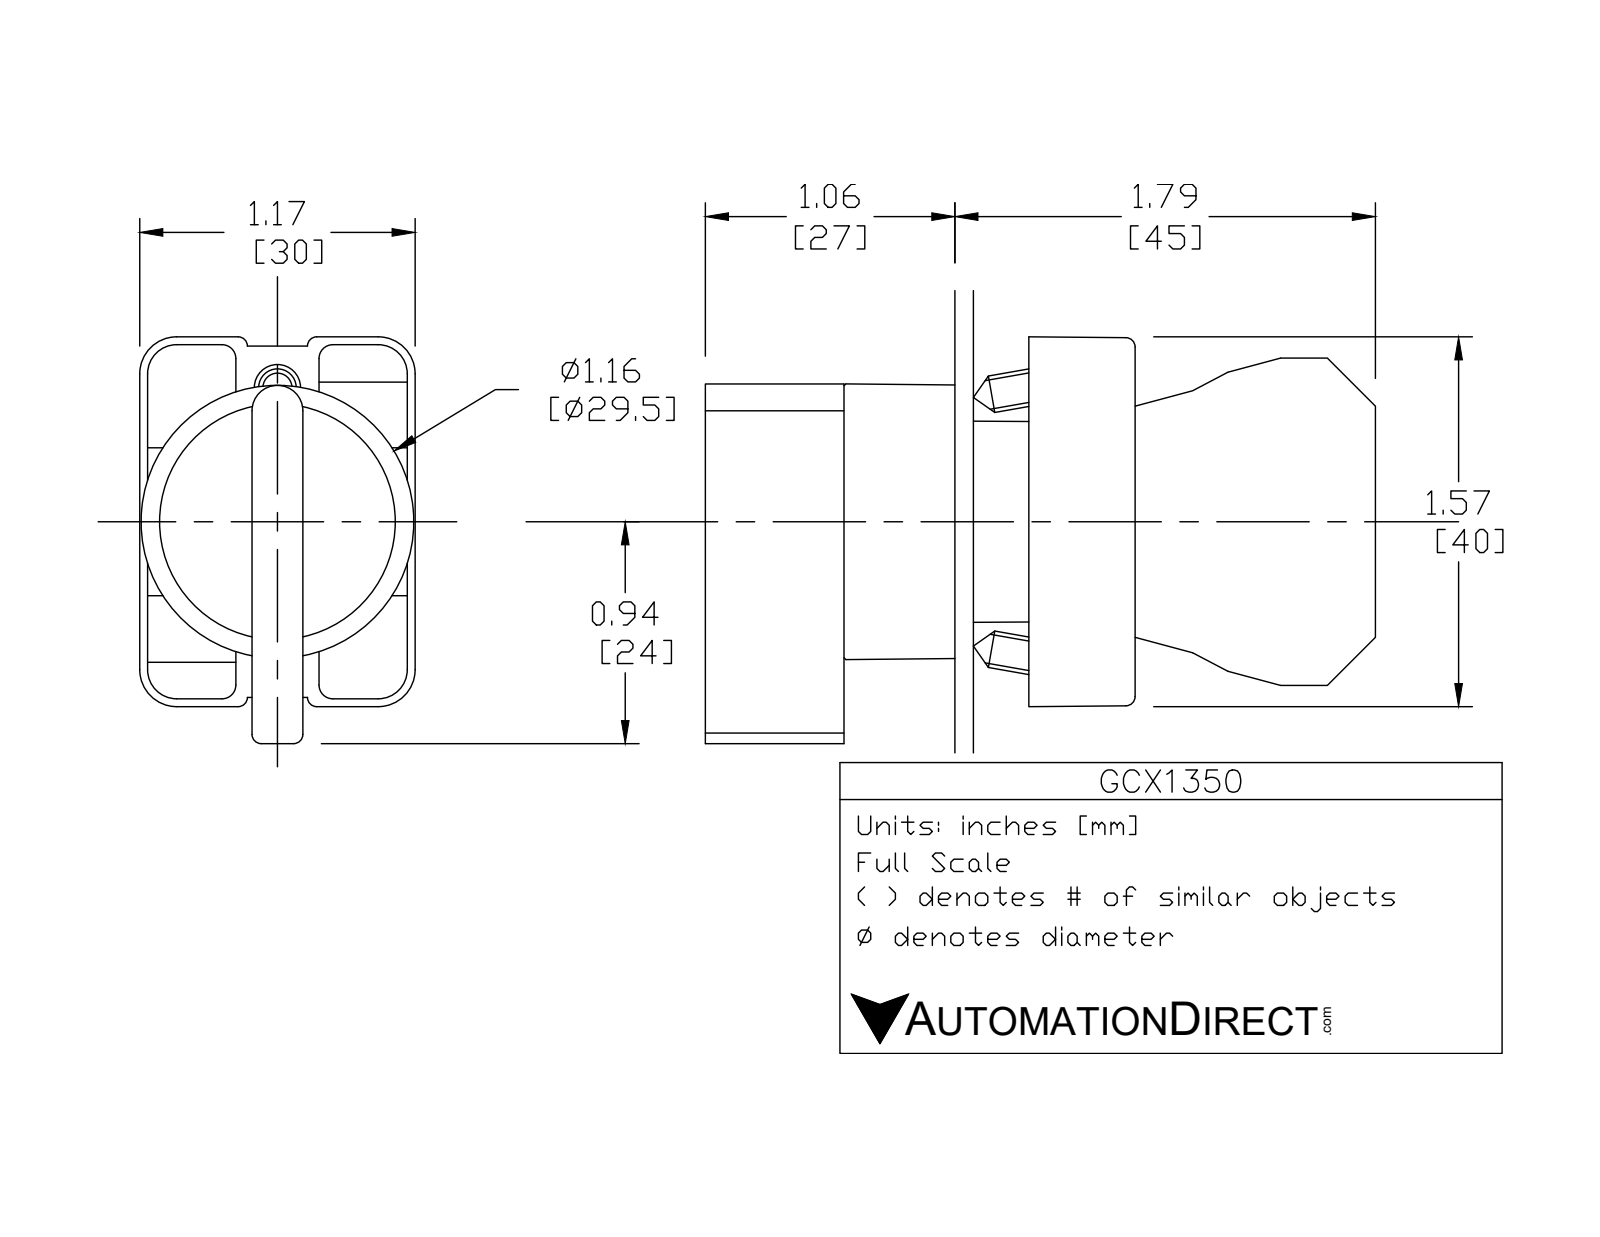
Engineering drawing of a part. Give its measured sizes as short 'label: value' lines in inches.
name: ecx1029; GCX1350 OPERATOR; ecx1040; GCX1350
written by: SolidWorks 2016 (AUTOMOTIVE_DESIGN)
unit: in
bodies: 6 solids, 396 faces (232 planar, 137 cylindrical, 27 other)
size: 2.78 × 1.752 × 1.177
volume: 1.929 in³; area: 29.25 in²
holes: 2× ⌀0.079, 2× ⌀0.124, 2× ⌀0.13, 1× ⌀0.087, 1× ⌀0.197, 1× ⌀0.878, 1× ⌀0.888, 1× ⌀1.024
bosses: 2× ⌀0.157, 1× ⌀1.175, 1× ⌀1.004, 1× ⌀0.945, 1× ⌀0.856, 1× ⌀0.78
rounds: 24× R0.059, 12× R0.041, 12× R0.124, 12× R0.157, 6× R0.039, 2× R0.128, 1× R0.02, 1× R0.063
face distances: 0.72, 0.579, 0.472, 0.033, 0.474, 0.703, 0.031, 0.124, 1.193, 1.024
hole spacings: 0.236, 0.544, 0.472, 0.49
